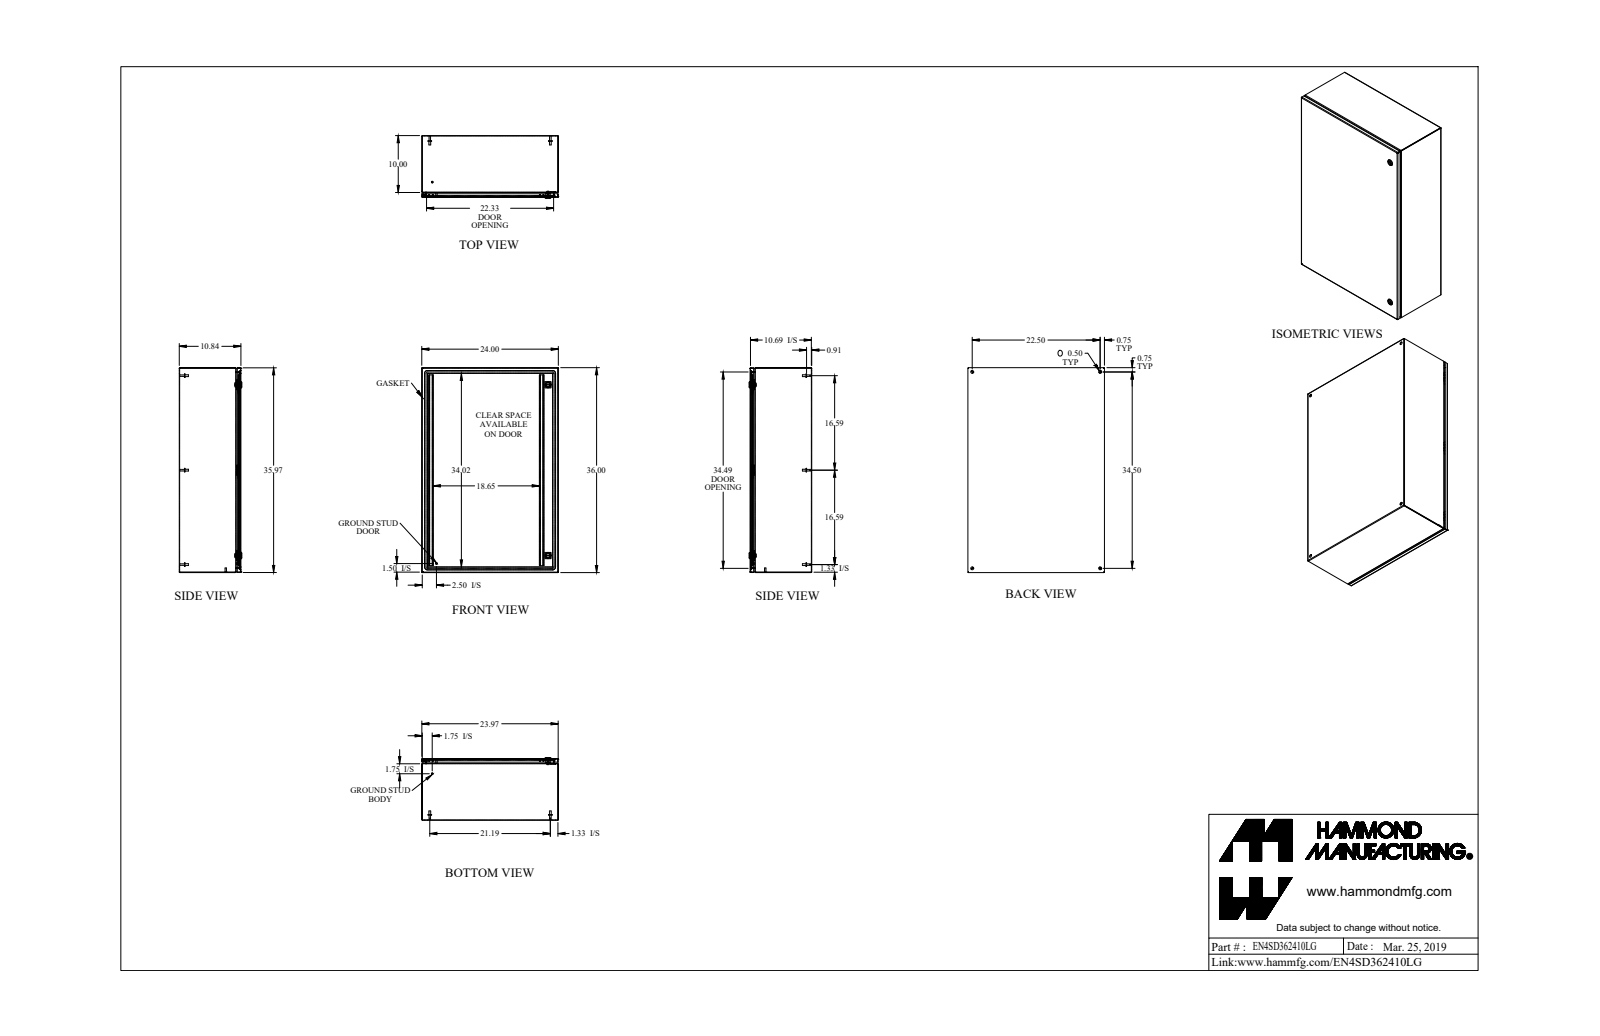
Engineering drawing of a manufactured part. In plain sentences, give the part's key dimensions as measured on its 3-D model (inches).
The part is named "EN4SD362410LG". Its 3-D file was written by "SolidWorks 2019 (AUTOMOTIVE_DESIGN)". It is 33 solids with 917 faces: 430 planar, 307 cylindrical and 180 other. Overall it measures 36 by 24 by 10.997 inches. Its volume is 244.1 cubic inches and its surface area 6 852 square inches. Round holes: 4 of diameter 0.5, 2 of diameter 0.232, 2 of diameter 0.625, 2 of diameter 0.785, 1 of diameter 0.172, 1 of diameter 0.24, 1 of diameter 0.242. Round bosses or shafts: 6 of diameter 0.625, 6 of diameter 0.313, 6 of diameter 0.27, 2 of diameter 1.1, 2 of diameter 0.525, 2 of diameter 0.281, 2 of diameter 0.25, 1 of diameter 0.455. Partial cylindrical surfaces (rounded edges, fillets, slot ends): 20 of radius 0.036, 20 of radius 0.108, 12 of radius 0.043, 12 of radius 0.081, 12 of radius 0.382, 8 of radius 19.003, 6 of radius 0.006, 6 of radius 0.062. The main face-to-face distances are 0.072, 10.765, 10.693, 10.837, 23.928, 35.928, 23.856, 24, 35.856, 36. The hole center spacings are 22.5, 34.5, 41.189, 2.493, 2.494, 21.544, 21.545, 29.999.
